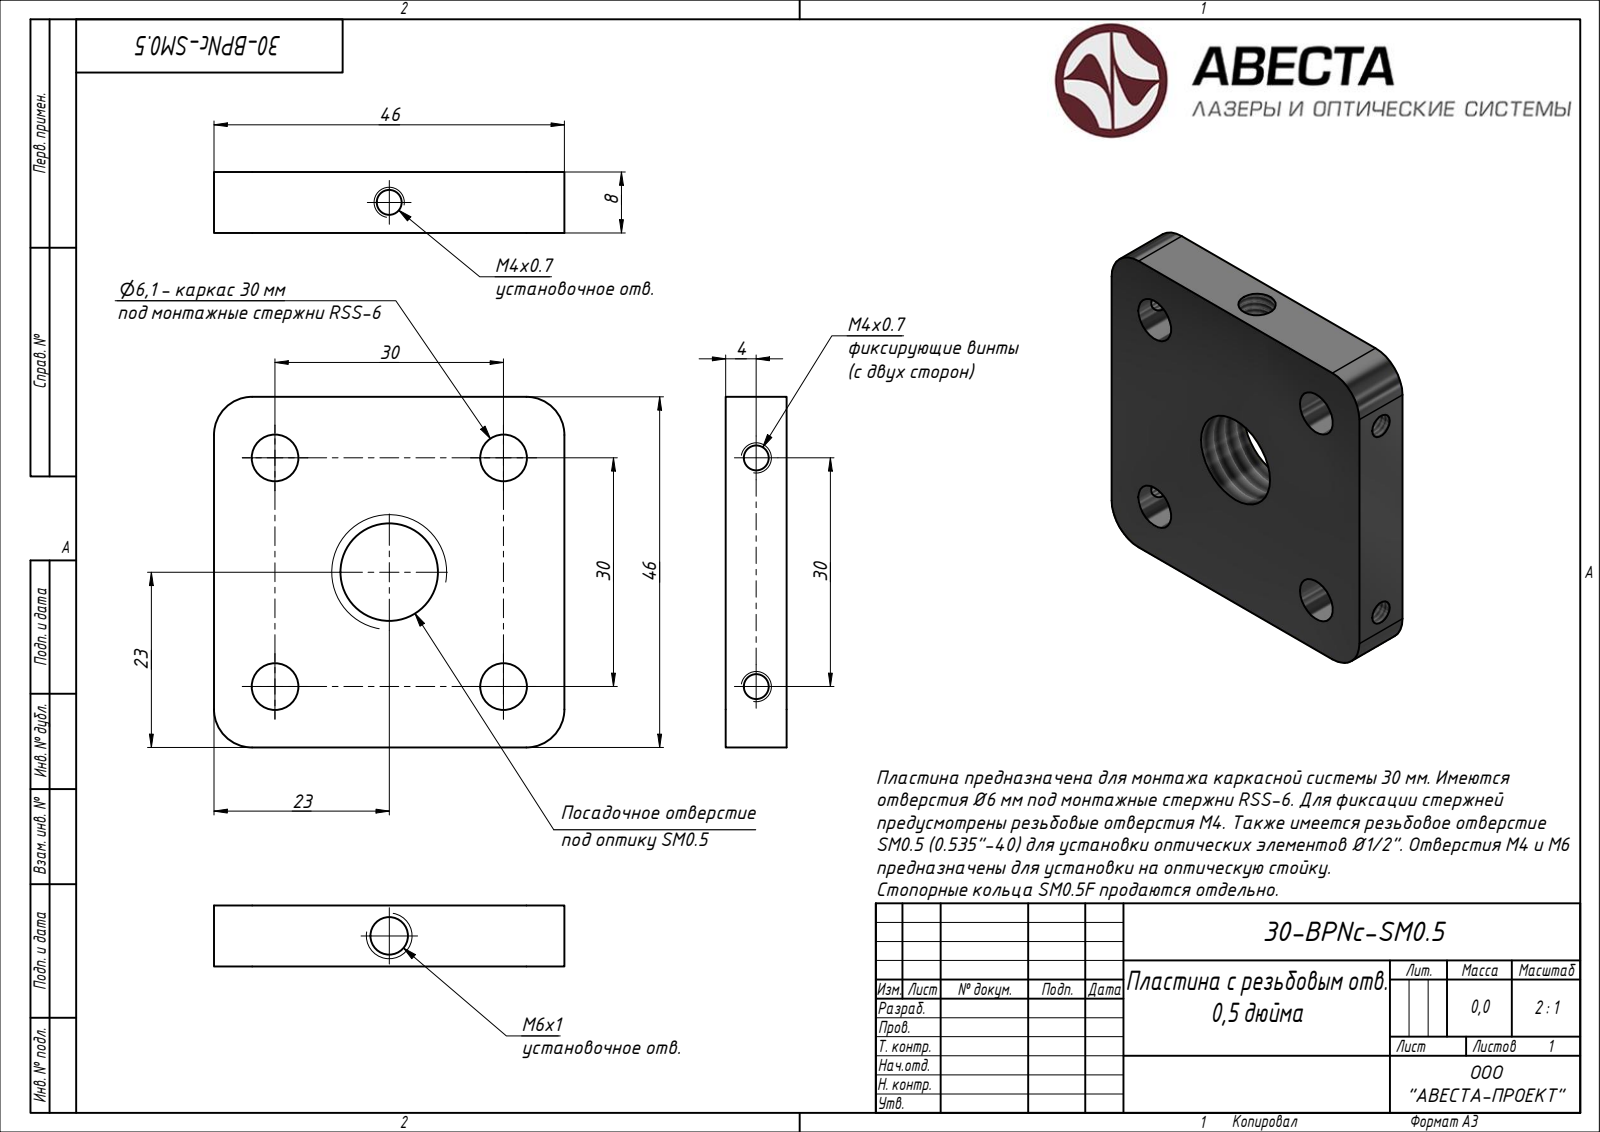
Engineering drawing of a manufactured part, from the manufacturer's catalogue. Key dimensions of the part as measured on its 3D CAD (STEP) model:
Part name (STEP PRODUCT): 30-BPNc-SM0,5
STEP written by: Autodesk Inventor 2020 (AUTOMOTIVE_DESIGN)
Units: millimetres
Bodies: 1 solid, 23 faces (8 planar, 15 cylindrical, 0 other)
Overall size (bounding box): 46 × 46 × 8
Volume: 14 464 mm³ · Surface area: 6 334 mm²
Round holes (diameter × count): ⌀6.1 ×4, ⌀3.24 ×3, ⌀4.92 ×1, ⌀12.78 ×1
Partial cylindrical surfaces — rounded edges, fillets, slot ends (radius × count): R5 ×4
Main face-to-face distances: 8, 46, 6, 40, 34
Hole centre spacings: 30, 21.21, 42.43
